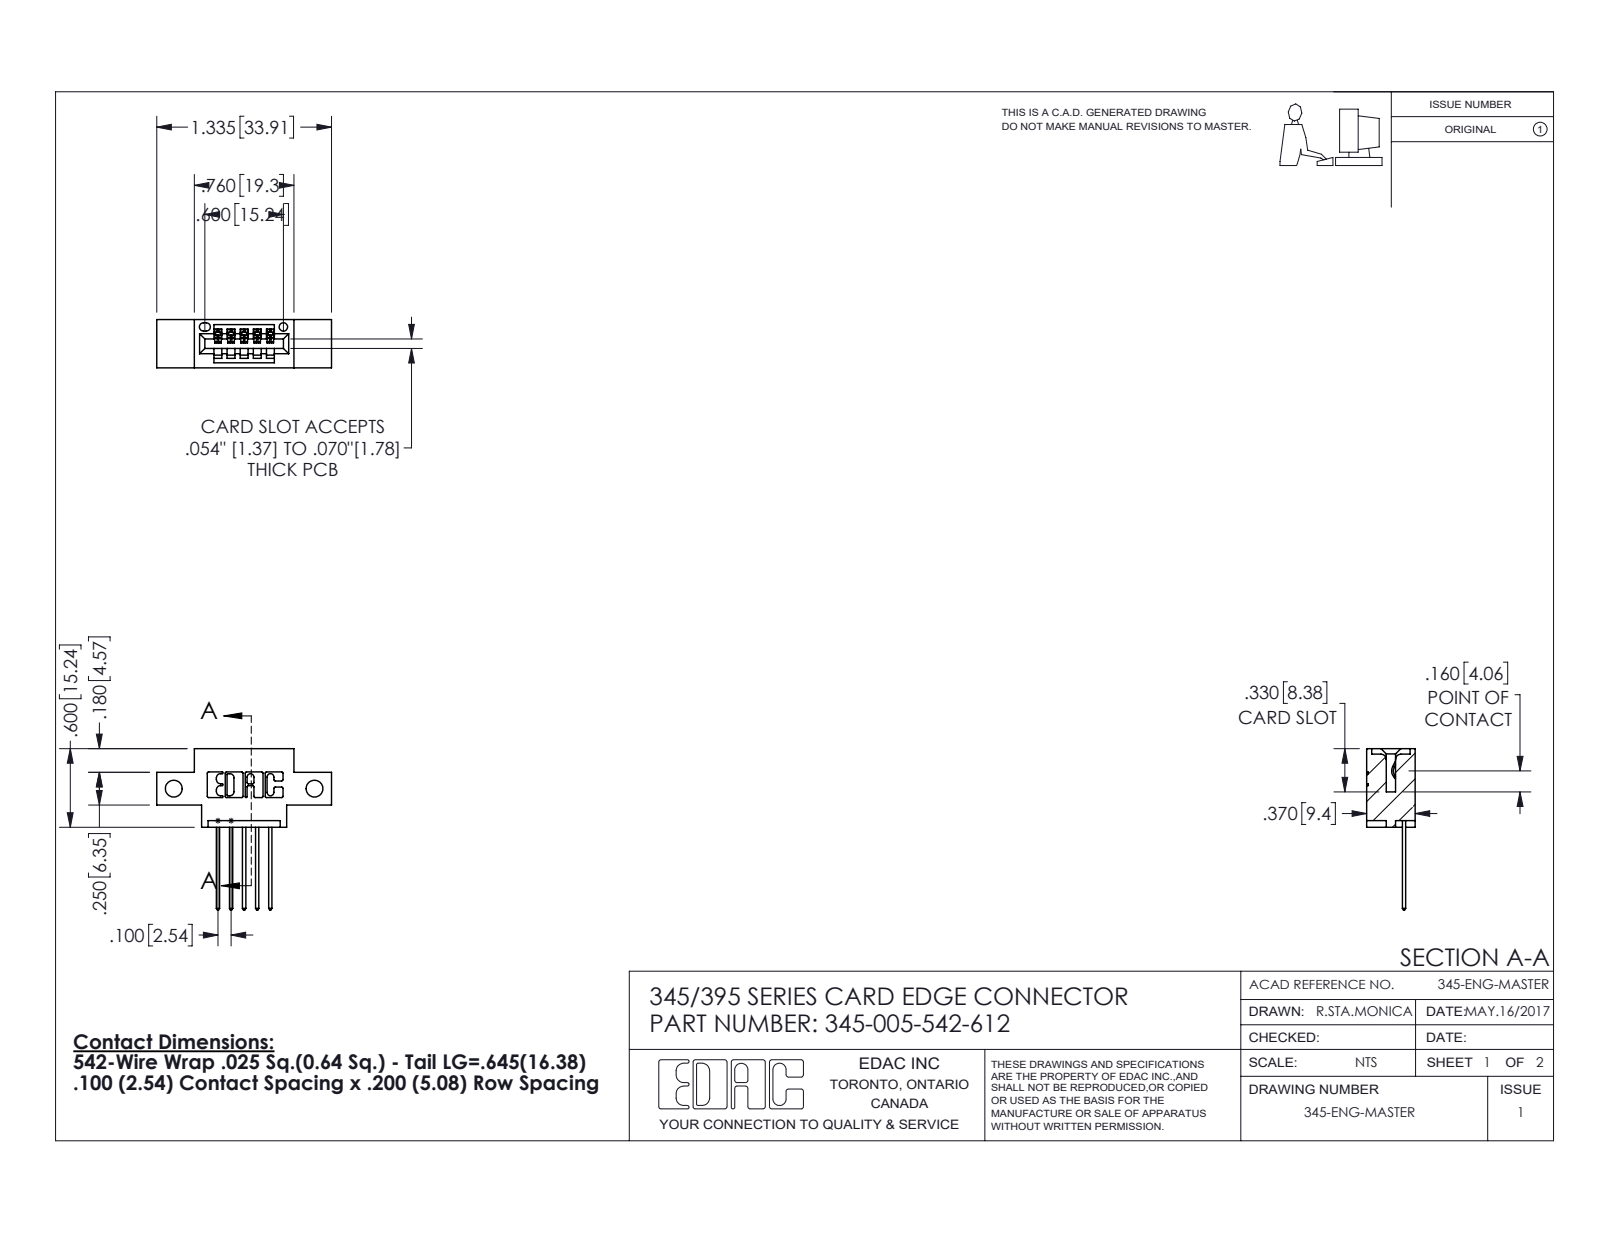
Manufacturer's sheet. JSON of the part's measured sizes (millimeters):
{"part_name": "345 Part_0.170 Offset - Side Mount; 345-005-542-612; 345-292-001_345-293-142", "step_written_by": "SolidWorks 2016 (CONFIG_CONTROL_DESIGN)", "units": "millimeters", "bodies": {"solids": 6, "faces": 420, "planar": 284, "cylindrical": 136, "other": 0}, "overall_size": [33.9, 31.3, 9.4], "volume_mm3": 2720, "surface_area_mm2": 3177, "round_holes": [[3.3, 2], [1.6, 1]], "partial_cylinders_radius": [[0.3, 22], [0.2, 10], [0.3, 10], [0.2, 6], [0.8, 6], [0.7, 3], [0.8, 2], [1, 2]], "face_to_face_distances": [9.4, 5.1, 7.6, 1.8, 2.5, 0.6, 6.4, 2.5, 6.9, 1.5], "hole_center_spacings": [27.3]}
